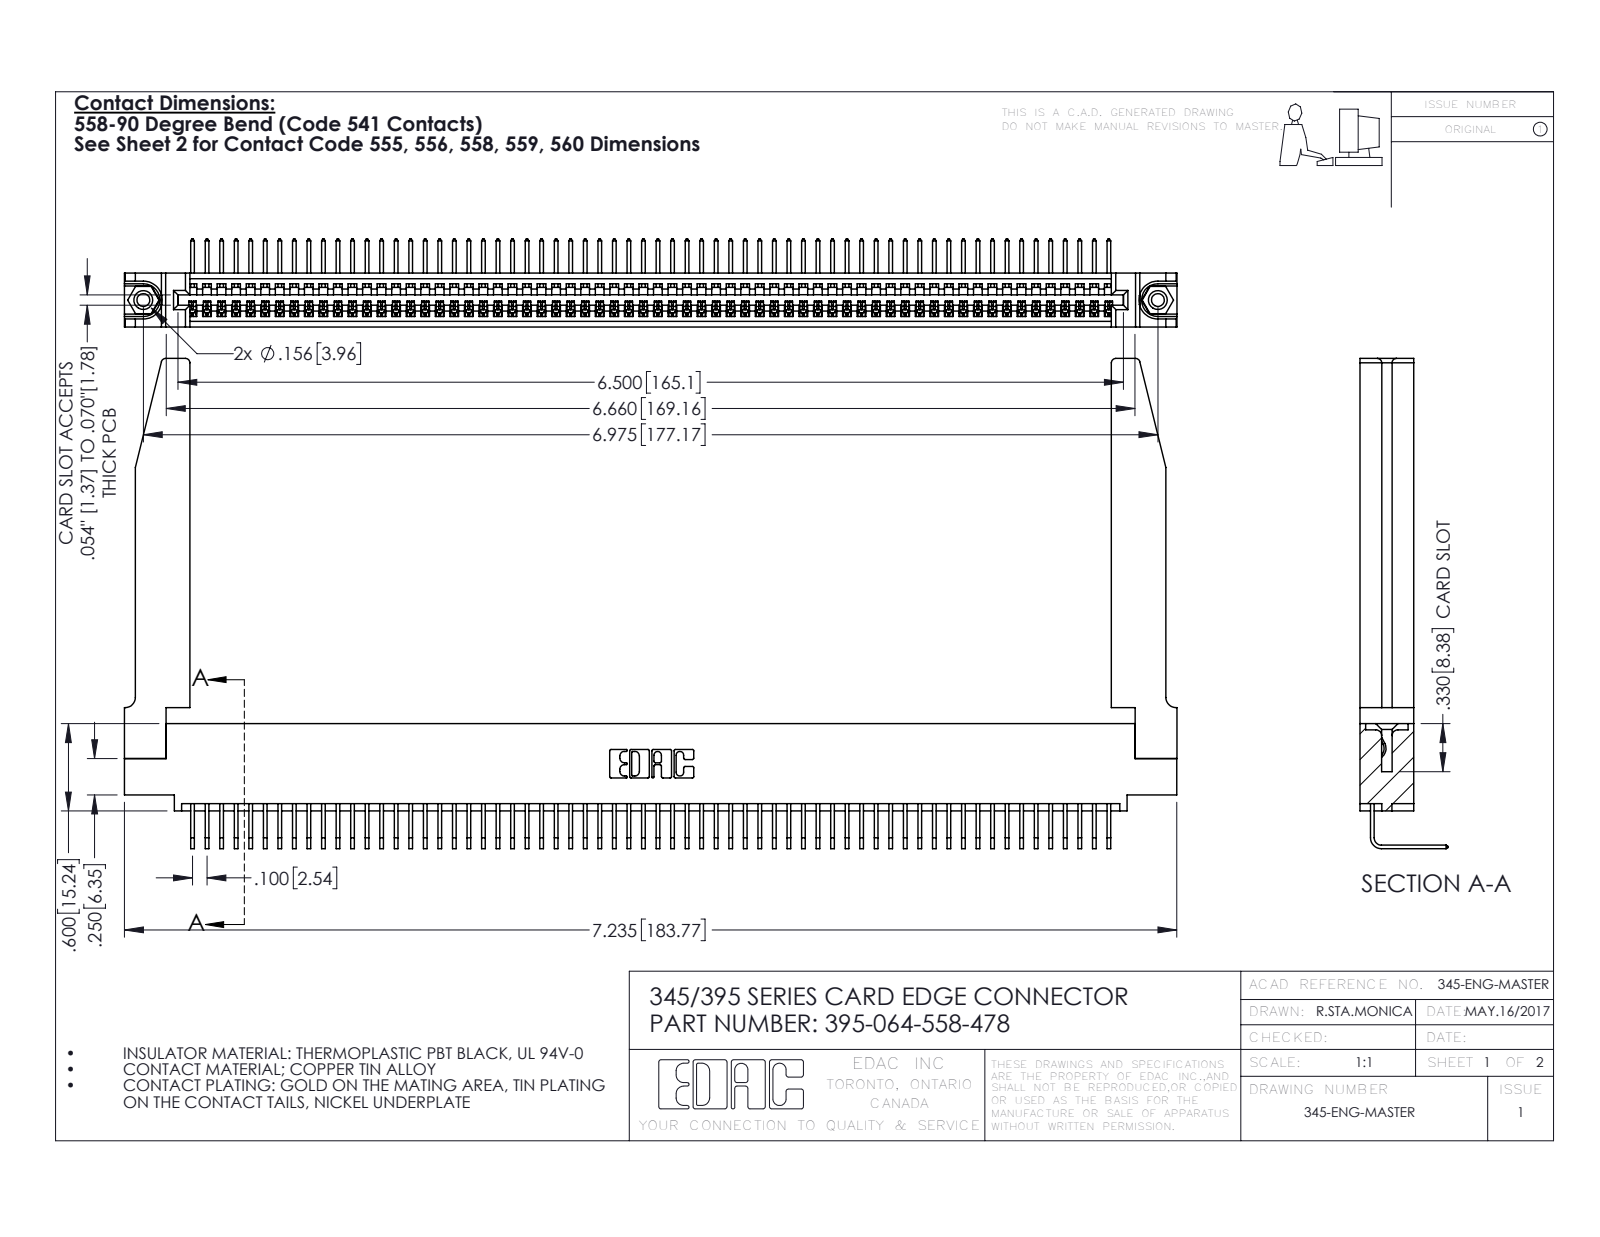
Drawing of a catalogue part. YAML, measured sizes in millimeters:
part_name: "345-292-001_558 Tail - 2; 345-250-001_345-250-001-102; 345 Part_0.110 Offset - 0.156 Dia-TH; 345-220-078_345-220-078 (+1 more)"
step_written_by: "SolidWorks 2016 (CONFIG_CONTROL_DESIGN)"
units: millimeters
bodies: {solids: 69, faces: 4204, planar: 2914, cylindrical: 1238, other: 52}
overall_size: [183.8, 85.6, 15.4]
volume: 25550
surface_area: 32100
round_holes:
  - {diameter: 2.3, count: 2}
  - {diameter: 3.2, count: 2}
  - {diameter: 4, count: 2}
  - {diameter: 1.6, count: 1}
round_bosses_or_shafts:
  - {diameter: 3.9, count: 2}
partial_cylinders:
  - {radius: 0.2, count: 128}
  - {radius: 0.3, count: 22}
  - {radius: 0.8, count: 8}
  - {radius: 0.2, count: 6}
  - {radius: 0.8, count: 6}
  - {radius: 0.7, count: 3}
  - {radius: 0.8, count: 2}
  - {radius: 1, count: 2}
face_to_face_distances: [1.8, 9.4, 7.6, 2.5, 6.9, 0.6, 5.1, 5.7, 3.8, 3.8]
hole_center_spacings: [6.9, 171.2, 177.2]
